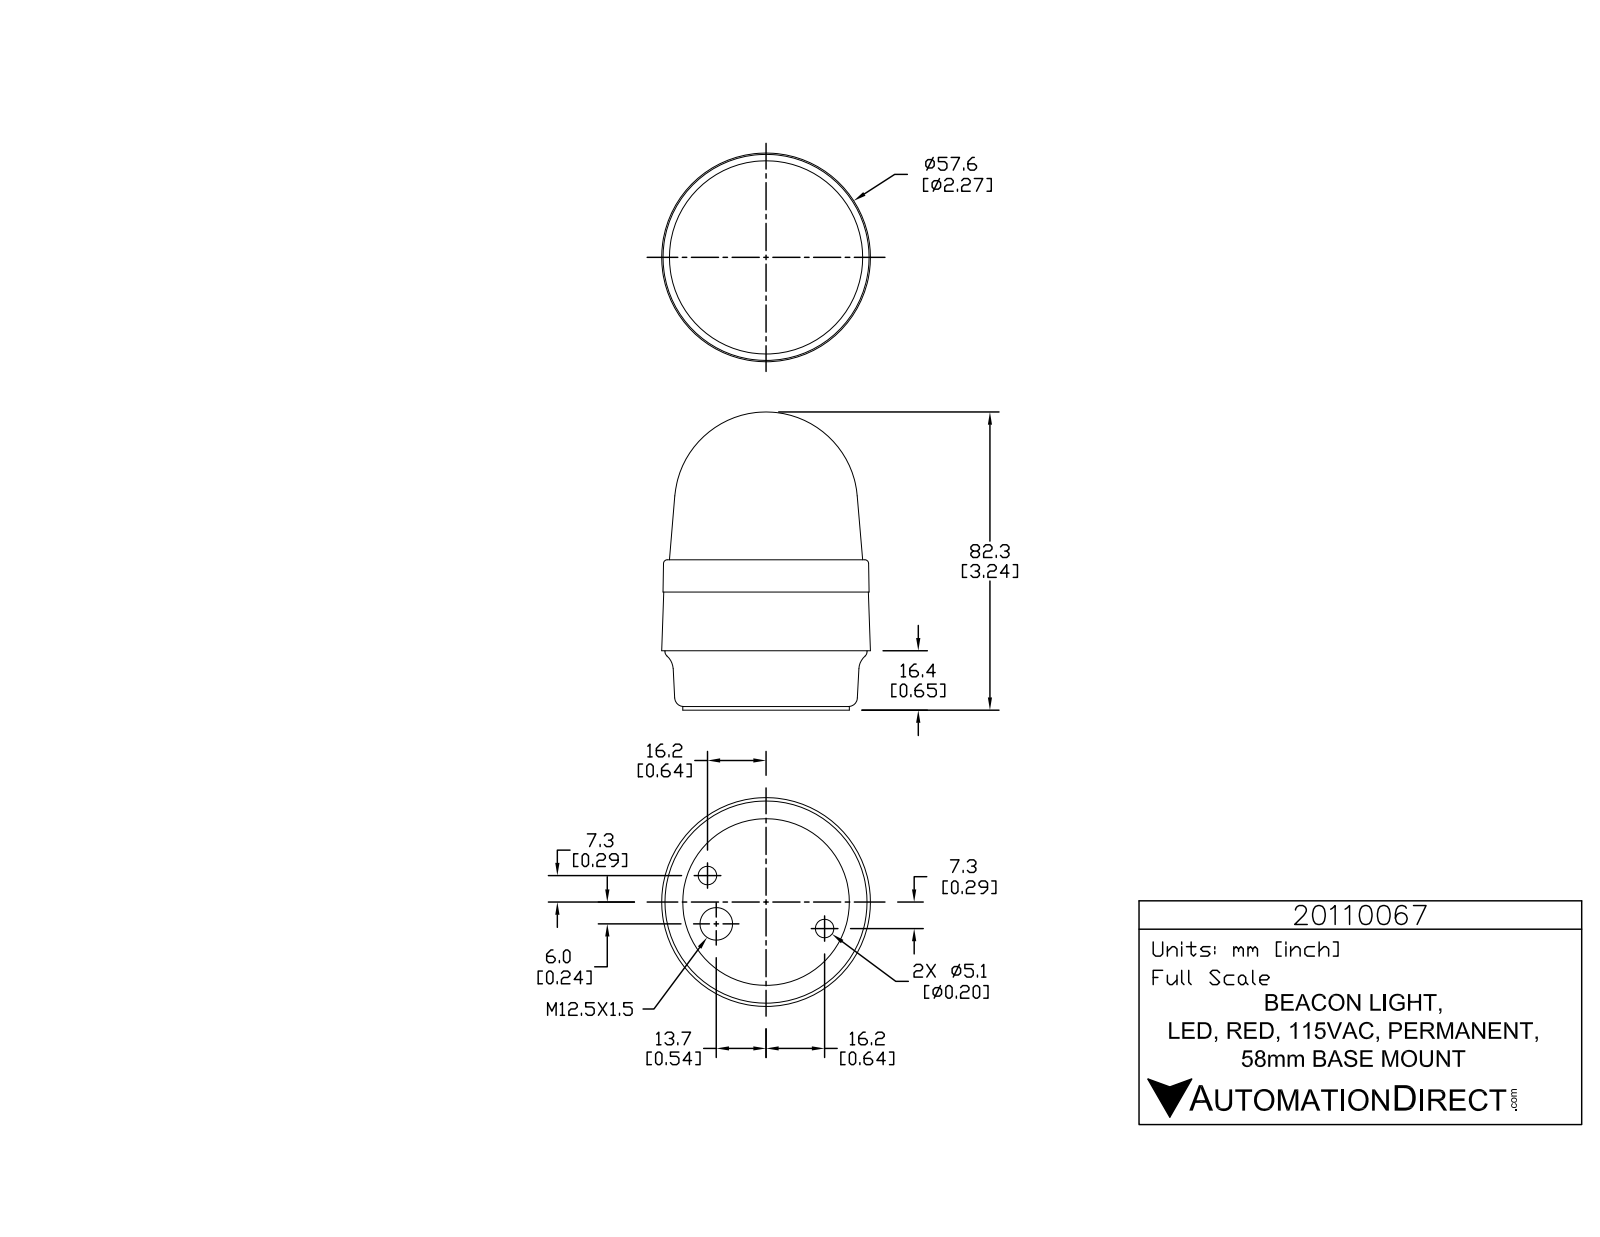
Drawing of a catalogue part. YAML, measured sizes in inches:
part_name: "20110067"
step_written_by: "SolidWorks 2015 (AUTOMOTIVE_DESIGN)"
units: inches
bodies: {solids: 1, faces: 763, planar: 527, cylindrical: 145, other: 91}
overall_size: [3.24, 2.269, 2.269]
volume: 10.03
surface_area: 25.2
round_holes:
  - {diameter: 0.039, count: 3}
  - {diameter: 0.201, count: 2}
  - {diameter: 0.354, count: 1}
round_bosses_or_shafts:
  - {diameter: 0.226, count: 3}
  - {diameter: 0.056, count: 3}
  - {diameter: 2.197, count: 1}
  - {diameter: 1.811, count: 1}
partial_cylinders:
  - {radius: 0.008, count: 6}
  - {radius: 0.008, count: 6}
  - {radius: 0.008, count: 6}
  - {radius: 0.131, count: 6}
  - {radius: 0.004, count: 3}
  - {radius: 0.005, count: 3}
  - {radius: 0.007, count: 3}
  - {radius: 0.008, count: 3}
face_to_face_distances: [0.646, 0.039, 0.606, 1.634, 1.594, 0.988, 1.283, 1.244, 0.638, 0.35]
hole_center_spacings: [0.534, 1.179, 1.398]
